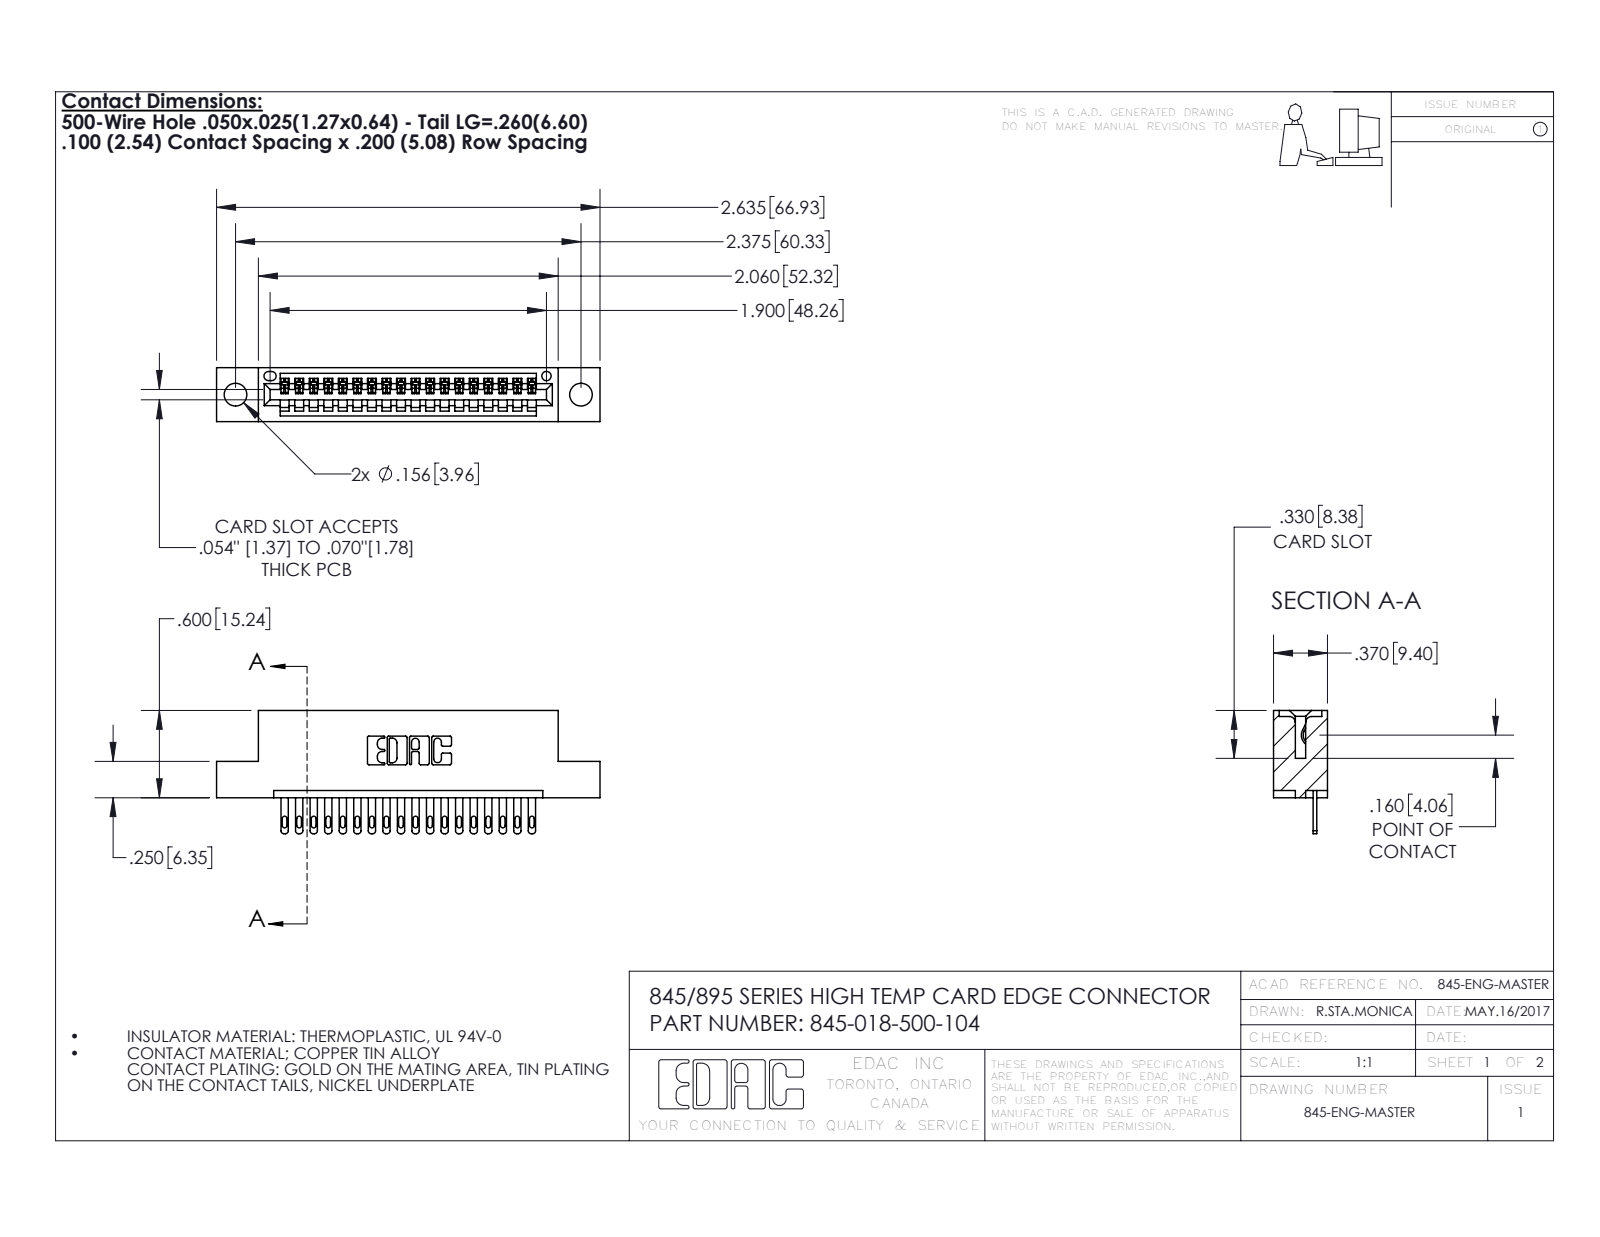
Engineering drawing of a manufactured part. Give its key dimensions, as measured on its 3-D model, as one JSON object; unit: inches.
{"part_name": "345-292-001_345-293-100; 345-018-500-104; 345 Part_Flush Mounting Lugs - 0.156 Dia-TH", "step_written_by": "SolidWorks 2016 (CONFIG_CONTROL_DESIGN)", "units": "inches", "bodies": {"solids": 19, "faces": 1098, "planar": 692, "cylindrical": 406, "other": 0}, "overall_size": [2.635, 0.847, 0.37], "volume_in3": 0.371, "surface_area_in2": 11.79, "round_holes": [[0.156, 2], [0.064, 1]], "partial_cylinders_radius": [[0.006, 36], [0.016, 36], [0.02, 36], [0.01, 22], [0.007, 6], [0.031, 6], [0.026, 3], [0.031, 2]], "face_to_face_distances": [0.298, 0.072, 0.2, 0.37, 0.098, 0.272, 0.025, 0.225, 0.1, 0.149], "hole_center_spacings": [0.27, 2.141, 2.375]}
